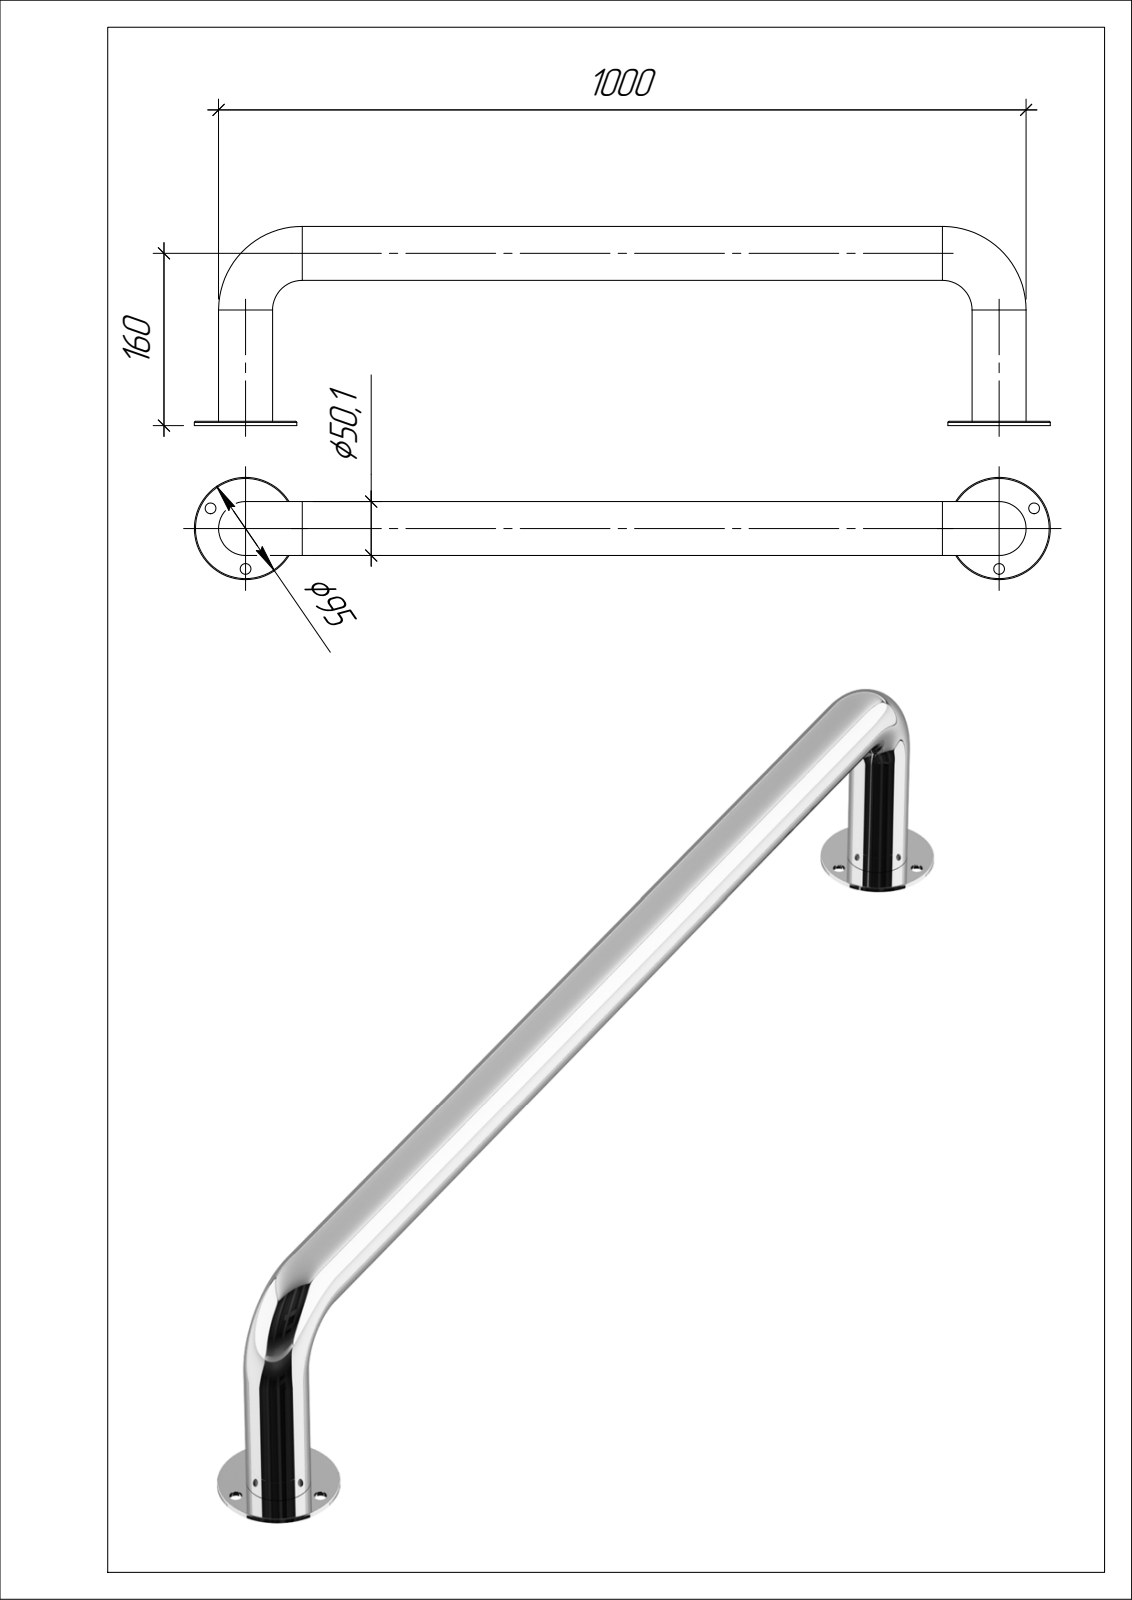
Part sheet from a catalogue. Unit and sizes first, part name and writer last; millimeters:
Units: millimetres
Overall size (bounding box): 1056.9 × 185.05 × 95
Round holes (diameter × count): ⌀10 ×6, ⌀48.1 ×3, ⌀49.1 ×2
Round bosses / shafts (diameter × count): ⌀50.1 ×3, ⌀95 ×2
Main face-to-face distances: 4
Hole centre spacings: 37.5, 64.95, 961.9, 64.96, 929.61, 931.12, 962.63, 994.56
Volume: 230 317 mm³ · Surface area: 405 806 mm²
Bodies: 3 solids, 28 faces (6 planar, 16 cylindrical, 6 other)
Part name (STEP PRODUCT): Сборка; Отбойник торговый для тележек; 95õ4
STEP written by: ASCON Math Kernel (AUTOMOTIVE_DESIGN)
